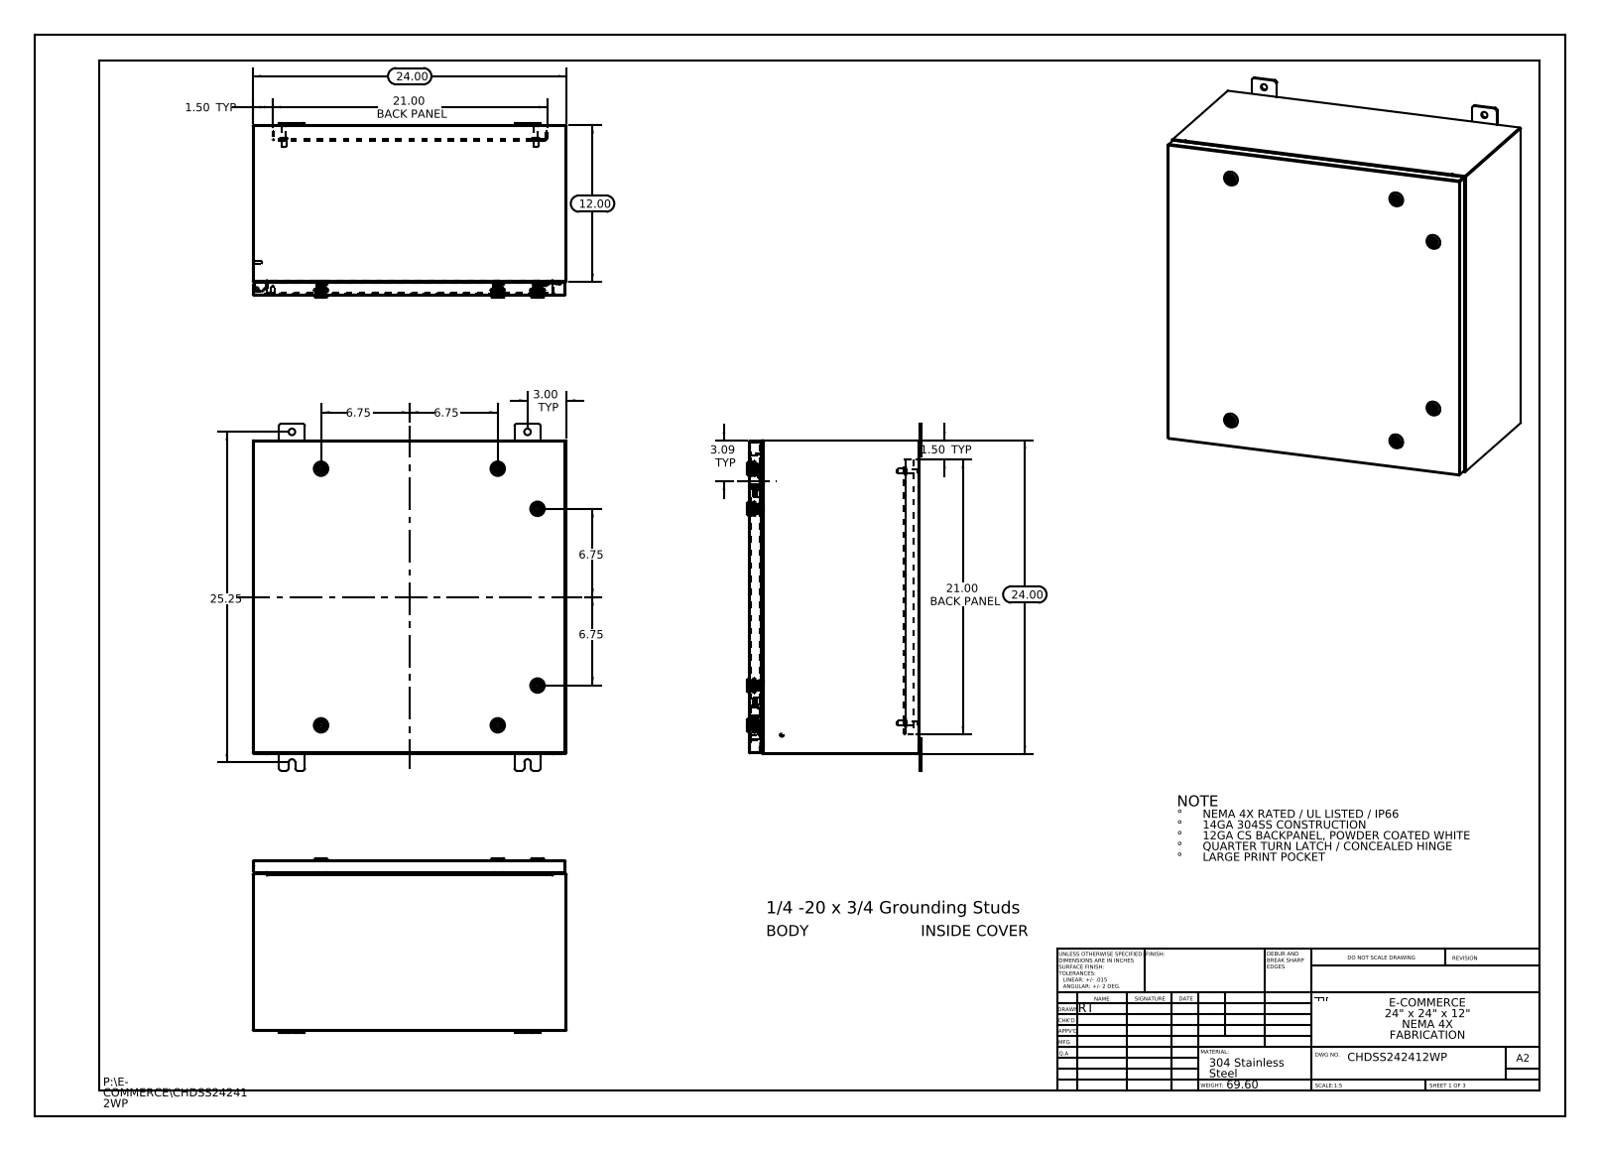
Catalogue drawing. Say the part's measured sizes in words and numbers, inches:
The part is named "HW-CLH-E5-8004_Cam-232112-U-Industrilas; Concealed Hinge enclosure side; CHDSS242412WP Backpanel; CHDSS242412WP Mounting Studs (+8 more)". Its 3-D file was written by "SolidWorks 2013 (CONFIG_CONTROL_DESIGN)". It is 55 solids with 5420 faces: 1592 planar, 1692 cylindrical and 2136 other. Overall it measures 26.5 by 24 by 13.356 inches. Its volume is 247.1 cubic inches and its surface area 6 219 square inches. Round holes: 8 of diameter 0.5, 6 of diameter 0.197, 6 of diameter 0.394, 6 of diameter 0.4, 6 of diameter 0.63, 6 of diameter 0.787, 4 of diameter 0.136, 1 of diameter 0.211. Round bosses or shafts: 8 of diameter 0.236, 6 of diameter 1.102, 6 of diameter 0.78, 6 of diameter 0.626, 6 of diameter 0.61, 6 of diameter 0.531, 6 of diameter 0.392, 6 of diameter 0.114. Partial cylindrical surfaces (rounded edges, fillets, slot ends): 198 of radius 0.006, 198 of radius 0.118, 72 of radius 0.028, 24 of radius 0.02, 24 of radius 0.19, 24 of radius 0.197, 20 of radius 0.013, 18 of radius 0.088. The main face-to-face distances are 0.075, 23.925, 0.074, 23.85, 24, 13.01, 12.935, 12.936, 12.861, 0.104. The hole center spacings are 13.5, 0.688, 1.858, 2.878, 3.065, 16.376, 16.815, 17.687.
